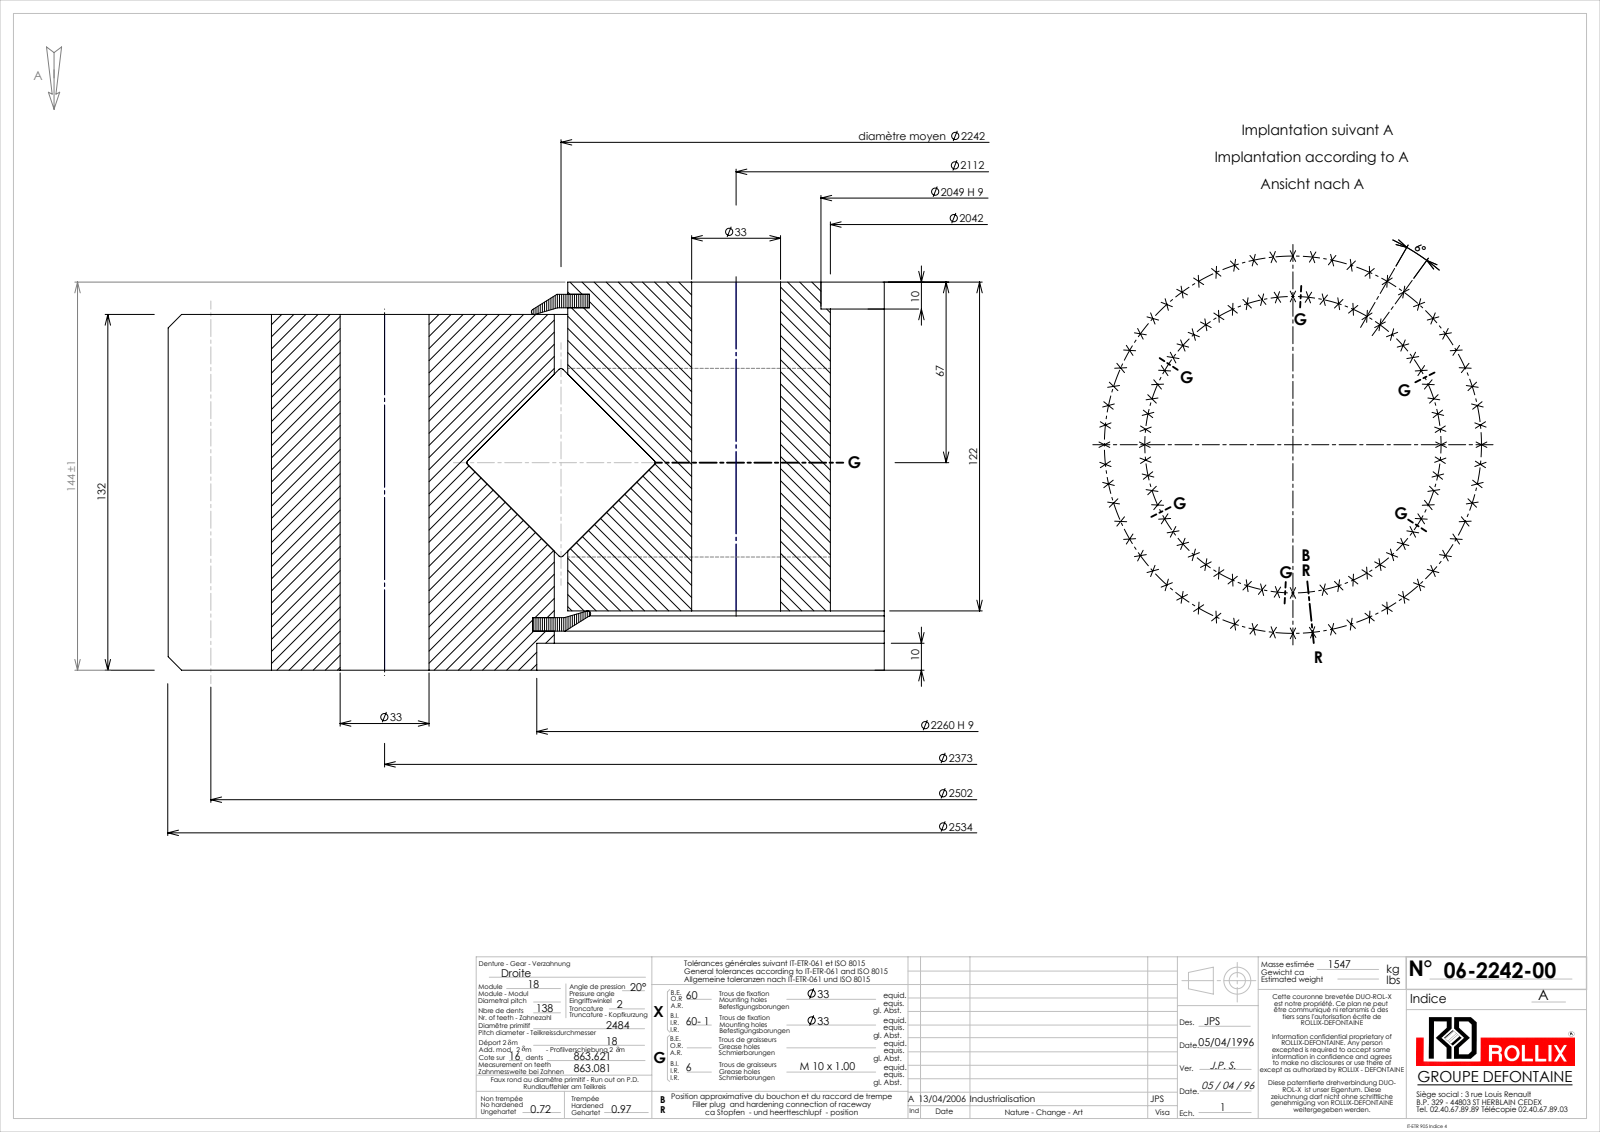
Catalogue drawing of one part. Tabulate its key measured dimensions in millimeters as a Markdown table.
| quantity | value |
| --- | --- |
| part name | 06-2242-00 |
| STEP written by | SolidWorks 2016 (CONFIG_CONTROL_DESIGN) |
| units | millimeters |
| bodies | 5 solids, 1165 faces (292 planar, 555 cylindrical, 318 other) |
| overall size | 2534 × 2533.68 × 144 |
| volume | 175 800 000 mm³ |
| surface area | 10 480 000 mm² |
| round holes (diameter × count) | 33 × 119, 9 × 6, 2042 × 1, 2049 × 1, 2221 × 1, 2247 × 1, 2260 × 1, 2263 × 1 |
| round bosses / shafts (diameter × count) | 2237 × 1, 50 × 1 |
| partial cylindrical surfaces (radius × count) | 1228.5 × 1, 1267 × 1 |
| main face-to-face distances | 132, 12, 122, 22, 110, 144, 5, 7.5, 117.5, 2.5 |
| hole center spacings | 371.22, 1077.32, 124.19, 1186.5, 248.05, 493.37, 614.18, 733.3 |
